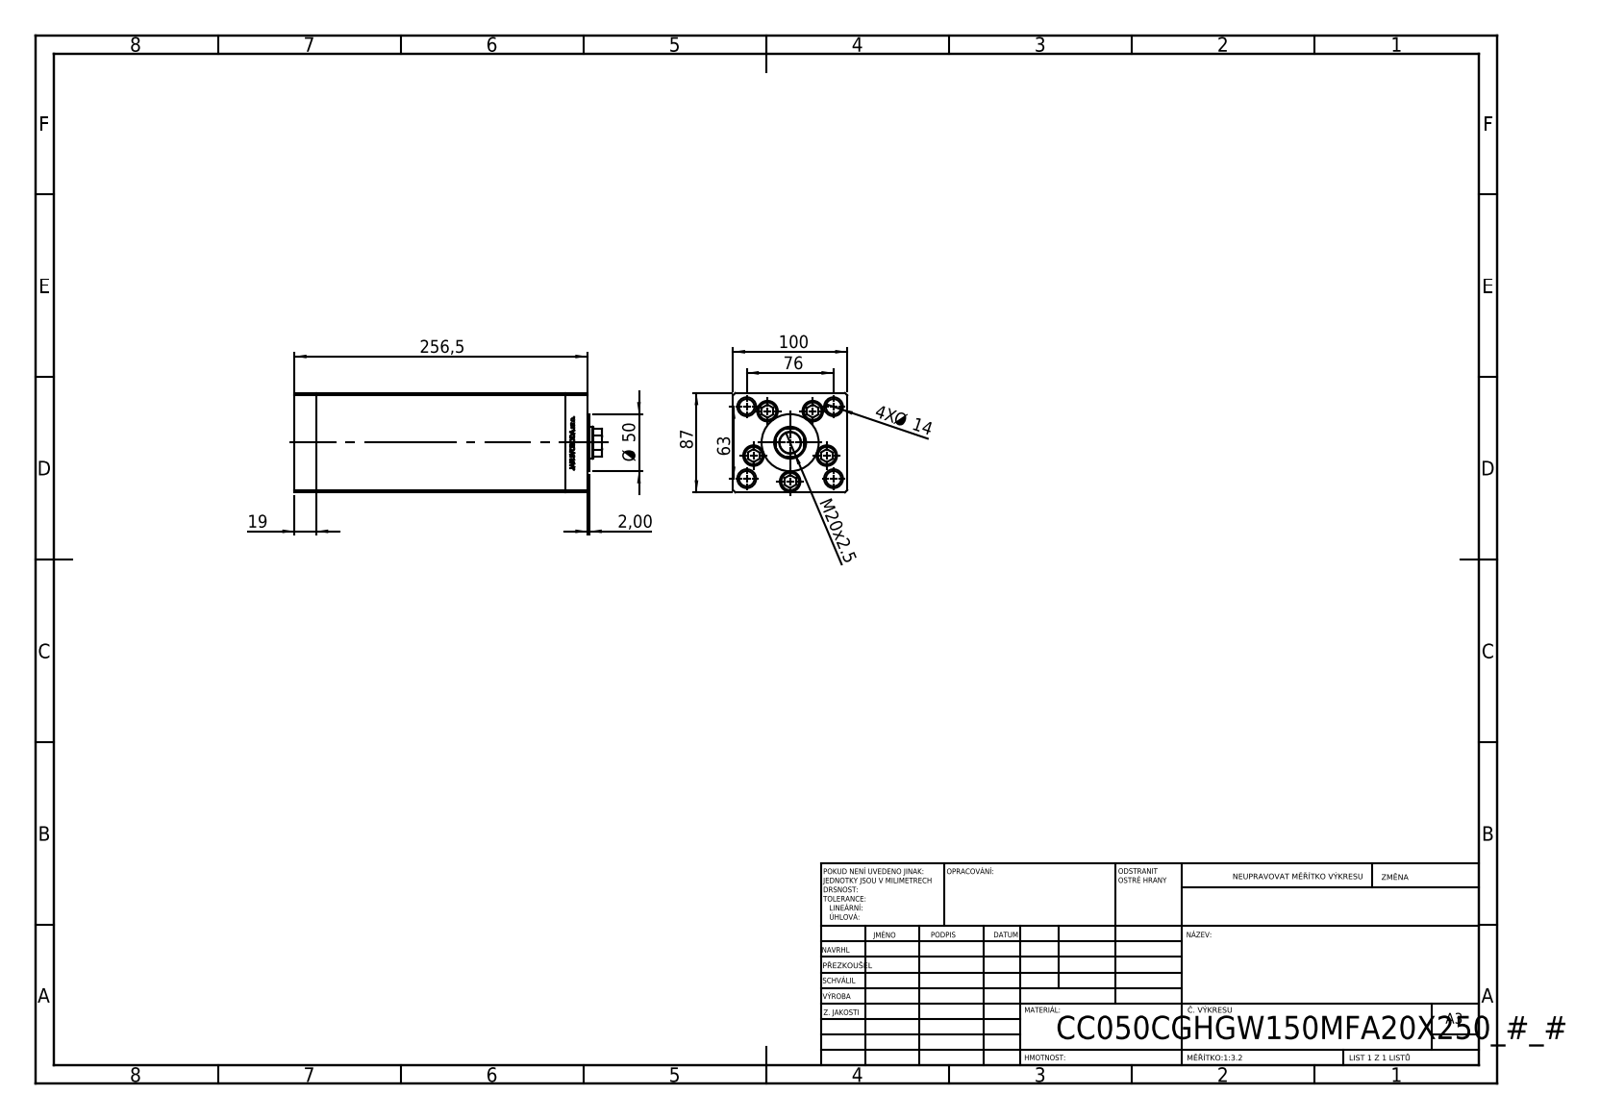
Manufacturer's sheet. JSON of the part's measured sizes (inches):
{"part_name": "V220C_VC_C; V220C BACK_C; V220C_C MIDDLE; ALLEN BOLT (+1 more)", "step_written_by": "SolidWorks 2019 (CONFIG_CONTROL_DESIGN)", "units": "inches", "bodies": {"solids": 13, "faces": 1186, "planar": 548, "cylindrical": 176, "other": 462}, "overall_size": [10.61, 3.937, 3.425], "volume_in3": 111.1, "surface_area_in2": 433.2, "round_holes": [[0.531, 9], [0.709, 5], [0.079, 4], [0.472, 4], [0.518, 4], [0.65, 4], [0.669, 1], [0.728, 1], [1.102, 1]], "round_bosses_or_shafts": [[0.315, 5], [0.669, 4], [1.969, 1]], "partial_cylinders_radius": [[0.037, 2], [0.531, 1]], "face_to_face_distances": [3.937, 3.425, 0.748, 8.602, 9.35, 1.348, 10.098, 8.75, 8.002, 0.6], "hole_center_spacings": [1.339, 1.943, 0.732, 0.828, 1.499, 1.546, 1.607, 1.702]}
